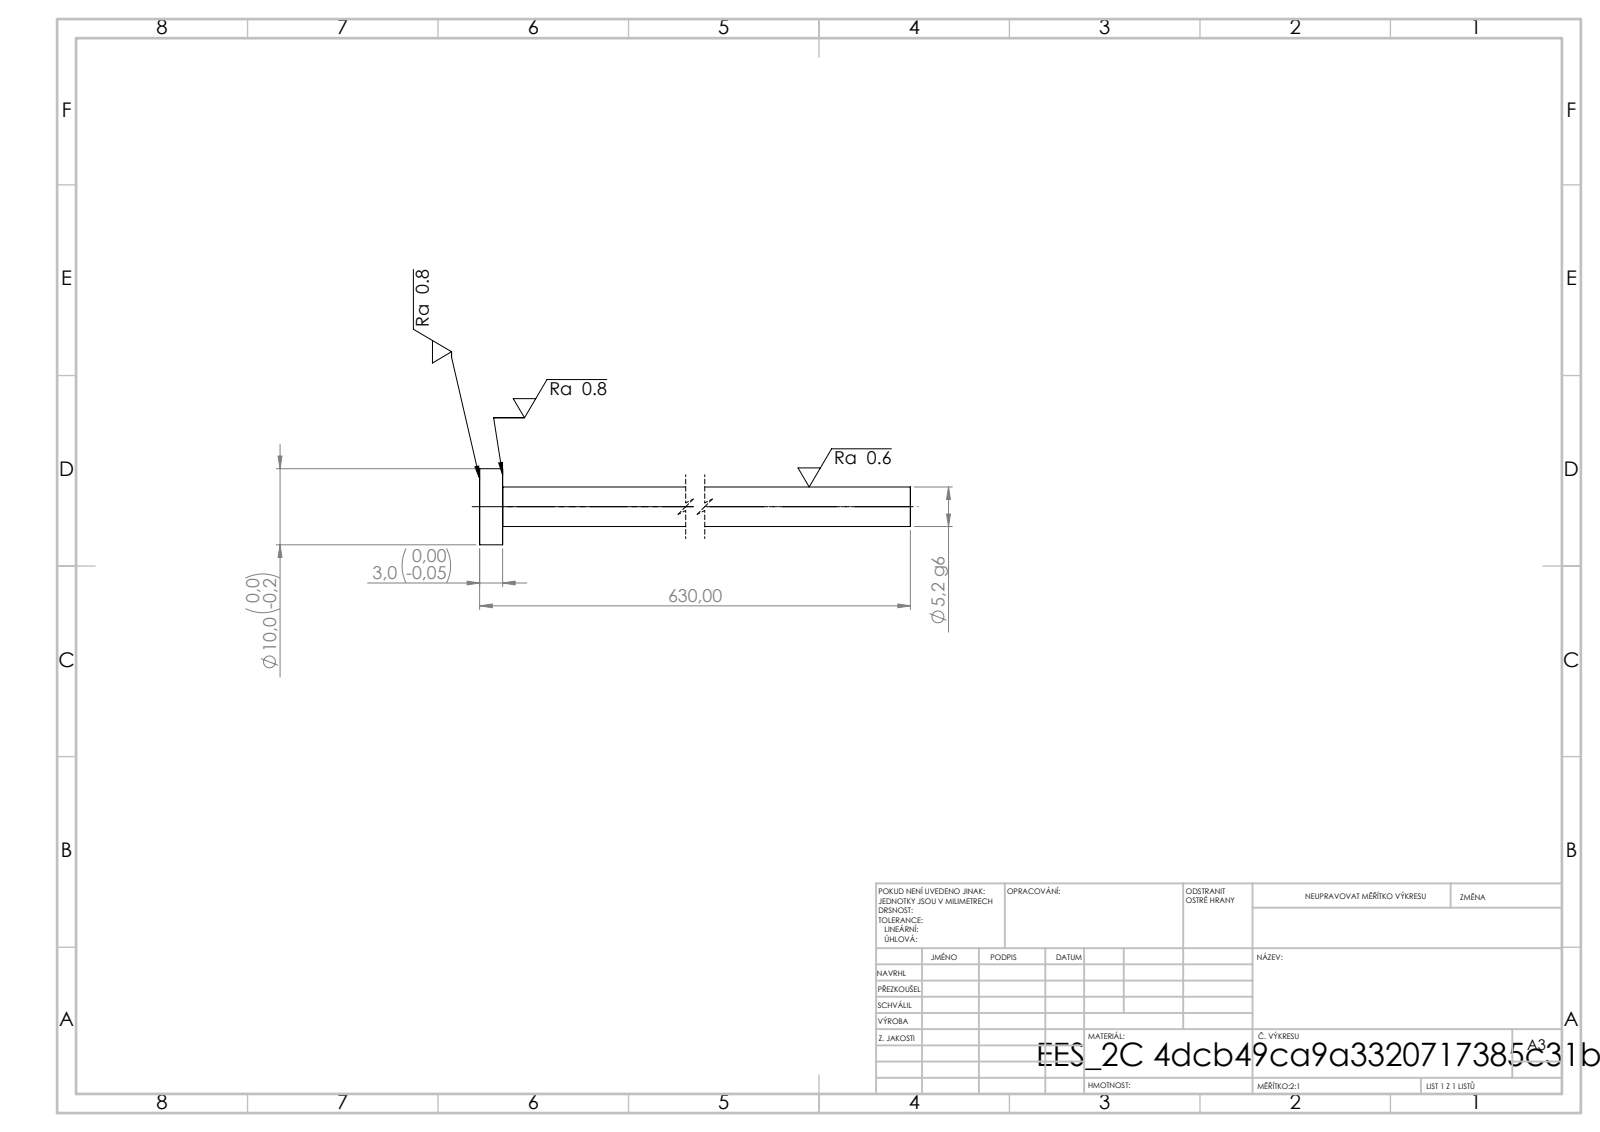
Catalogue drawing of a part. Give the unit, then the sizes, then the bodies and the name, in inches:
Units: inches
Overall size (bounding box): 24.803 × 0.394 × 0.394
Round bosses / shafts (diameter × count): ⌀0.394 ×1, ⌀0.205 ×1
Main face-to-face distances: 0.118, 24.803, 24.685
Volume: 0.827 in³ · Surface area: 16.27 in²
Bodies: 1 solid, 7 faces (3 planar, 4 cylindrical, 0 other)
STEP written by: SolidWorks 2019 (CONFIG_CONTROL_DESIGN)
